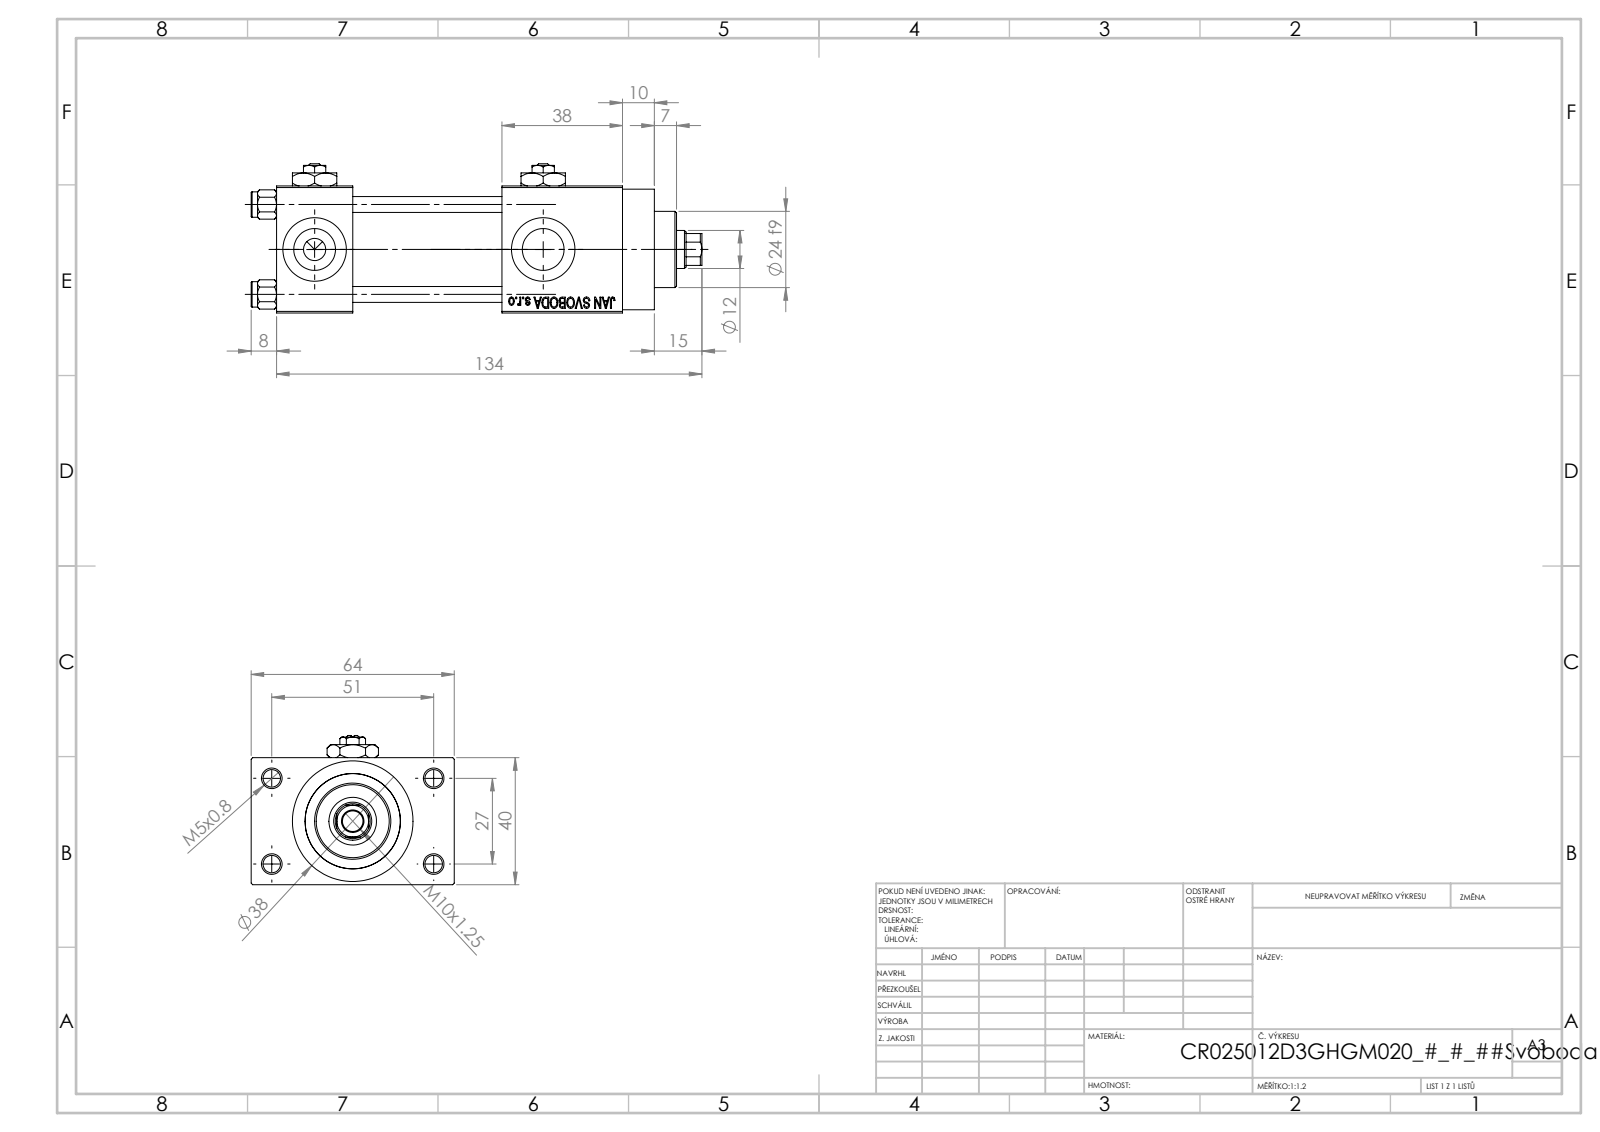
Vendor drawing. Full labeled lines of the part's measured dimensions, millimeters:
Part name (STEP PRODUCT): V215CR_D_Body; V215_VC_A; V215CR_D_TYCINKA; V215CR_VCP_D (+2 more)
STEP written by: SolidWorks 2019 (CONFIG_CONTROL_DESIGN)
Units: millimetres
Bodies: 13 solids, 1201 faces (542 planar, 99 cylindrical, 560 other)
Overall size (bounding box): 142 × 64 × 47
Volume: 172 659 mm³ · Surface area: 63 806 mm²
Round holes (diameter × count): ⌀20 ×5, ⌀5 ×4, ⌀5.5 ×4, ⌀13.16 ×4, ⌀7 ×3, ⌀6.5 ×1, ⌀12 ×1, ⌀15 ×1, ⌀25 ×1, ⌀30 ×1
Round bosses / shafts (diameter × count): ⌀8 ×4, ⌀38 ×1, ⌀31 ×1, ⌀24 ×1
Partial cylindrical surfaces — rounded edges, fillets, slot ends (radius × count): R5.5 ×1
Main face-to-face distances: 40, 12, 47, 52, 24, 71, 38, 85, 109, 64
Hole centre spacings: 11.37, 20.01, 28.3, 28.85, 29.89, 39.66, 48.34, 27
